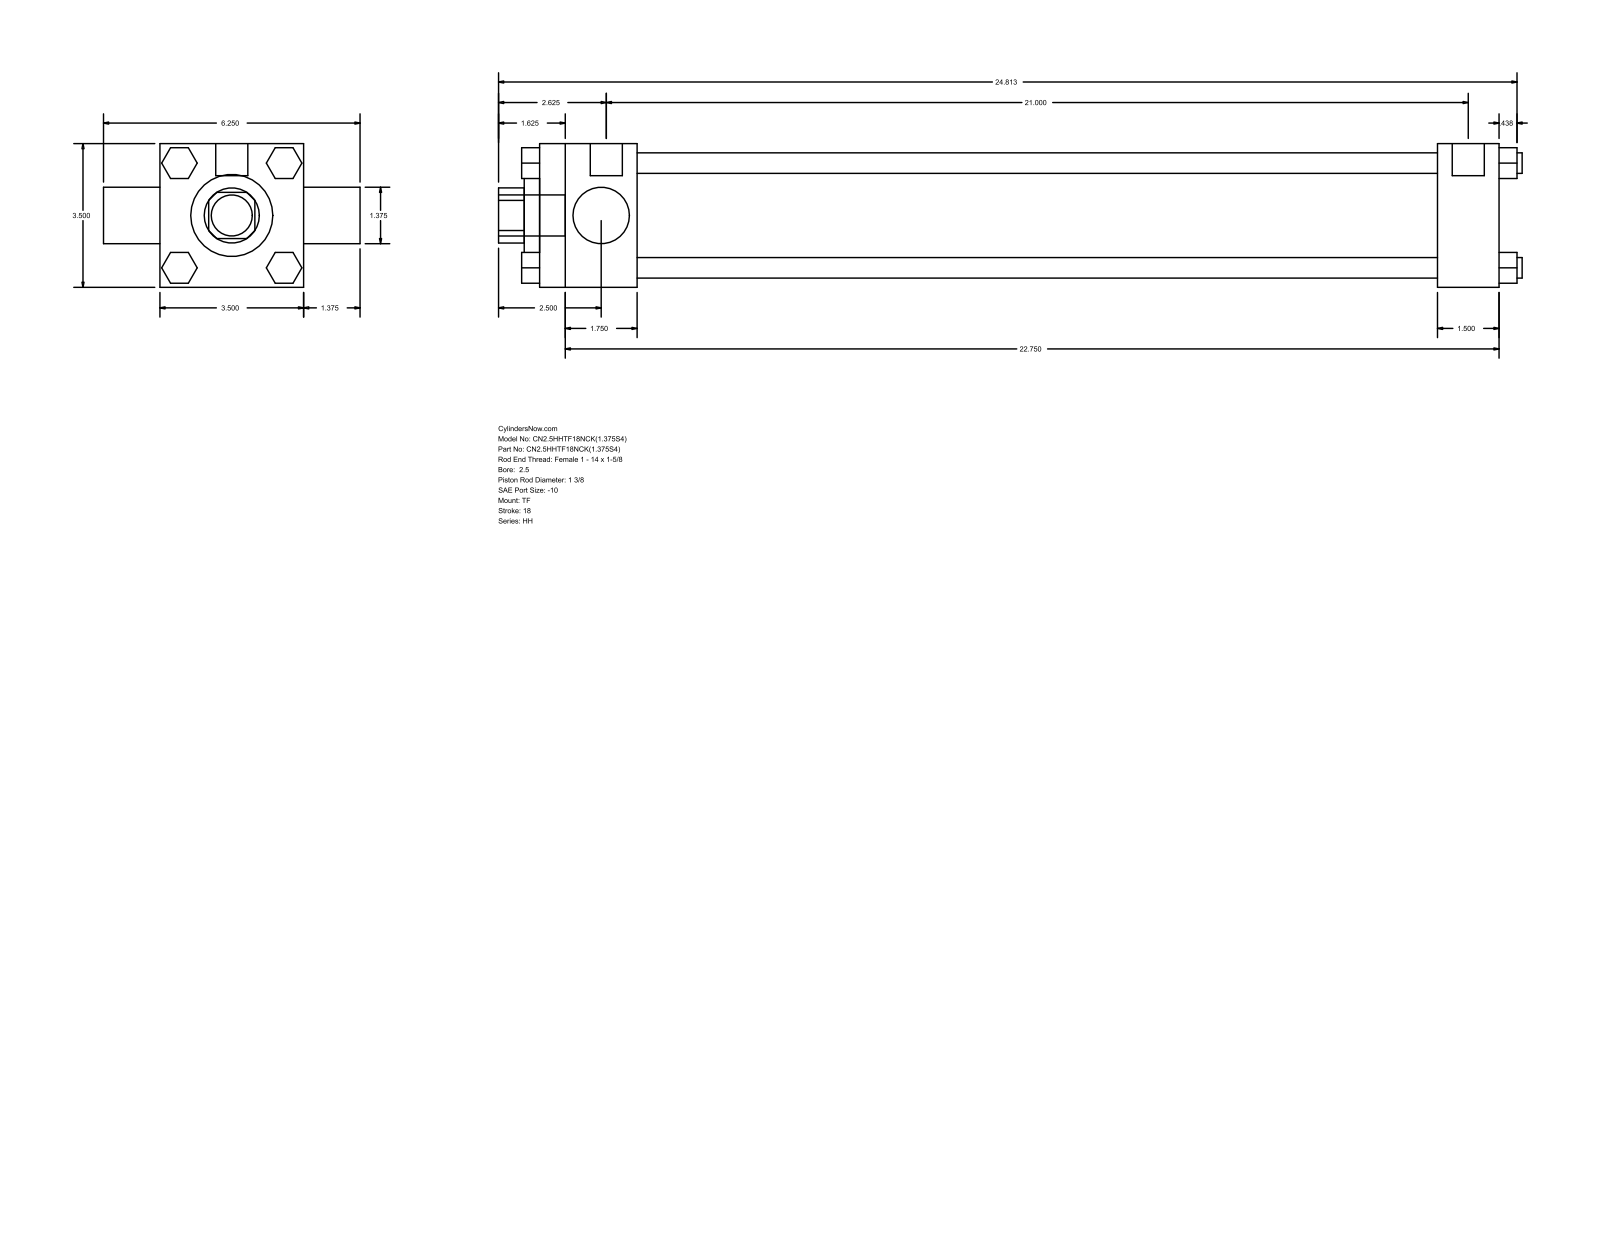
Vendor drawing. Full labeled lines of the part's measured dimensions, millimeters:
Part name (STEP PRODUCT): HH_TF__0250_1.375
STEP written by: GSSL Pune (CONFIG_CONTROL_DESIGN)
Units: millimetres
Bodies: 0 solids, 120 faces (92 planar, 28 cylindrical, 0 other)
Overall size (bounding box): 633.41 × 158.75 × 88.9
Round holes (diameter × count): ⌀34.92 ×2, ⌀50.8 ×1, ⌀73.03 ×1
Round bosses / shafts (diameter × count): ⌀12.7 ×4, ⌀5.56 ×3, ⌀19.84 ×2, ⌀25.4 ×1
Partial cylindrical surfaces — rounded edges, fillets, slot ends (radius × count): R17.06 ×1
Main face-to-face distances: 88.9, 593.72, 60.32, 533.4, 555.62, 495.3, 38.1, 19.05, 32.38, 56.09
